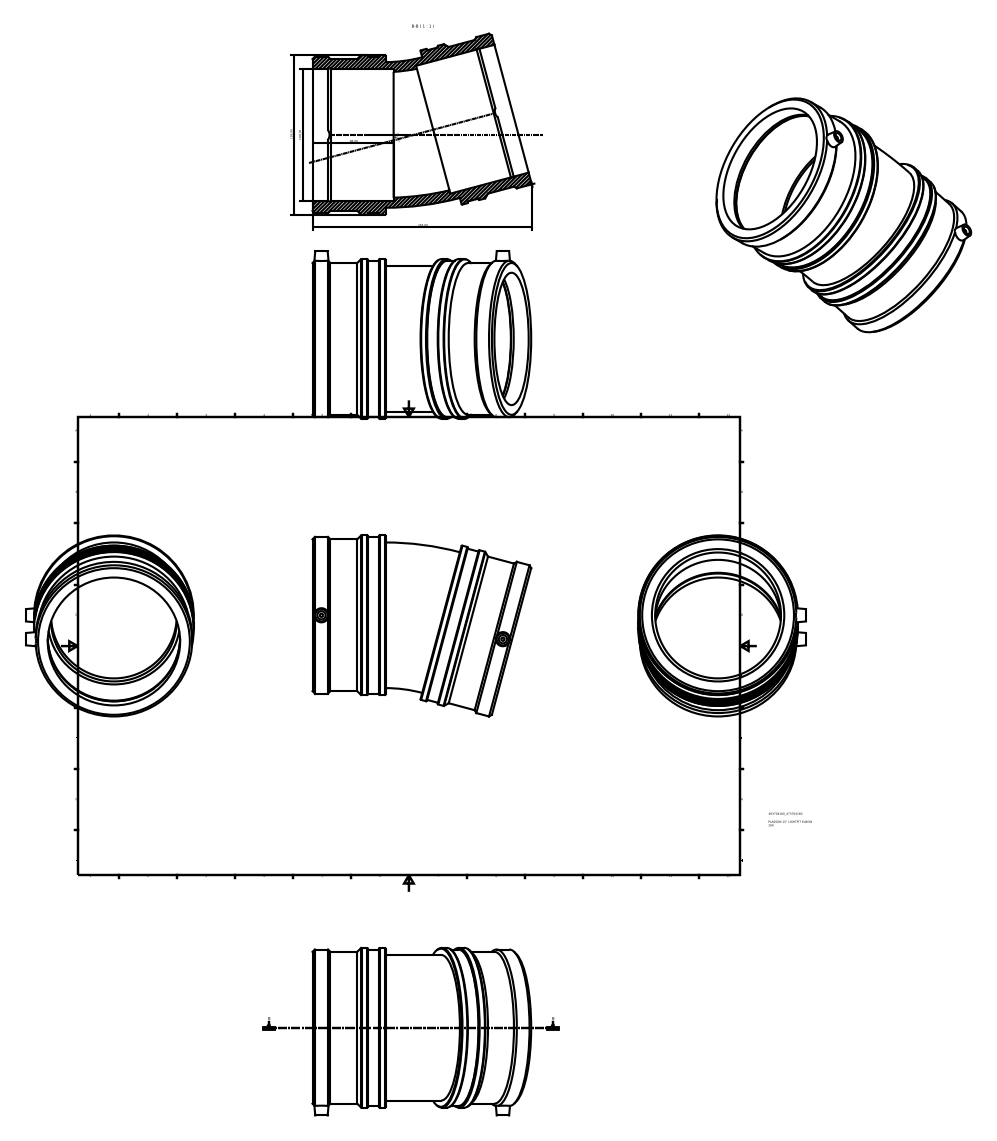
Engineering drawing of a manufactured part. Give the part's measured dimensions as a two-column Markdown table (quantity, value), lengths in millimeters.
| quantity | value |
| --- | --- |
| part name | 463704160_473704160 |
| STEP written by | Autodesk Inventor 2015 (AUTOMOTIVE_DESIGN) |
| units | millimeters |
| bodies | 1 solid, 58 faces (18 planar, 18 cylindrical, 22 other) |
| overall size | 264.27 × 218.78 × 202.5 |
| volume | 1 708 000 mm³ |
| surface area | 300 687 mm² |
| round holes (diameter × count) | 160 × 3, 10 × 2 |
| round bosses / shafts (diameter × count) | 189.14 × 3, 193 × 2, 183.47 × 2, 4 × 2 |
| main face-to-face distances | 88.2, 88.21, 9.81, 98.02, 98, 9.8, 66.75, 80.25, 13.5, 58 |
| hole center spacings | 221.22 |
